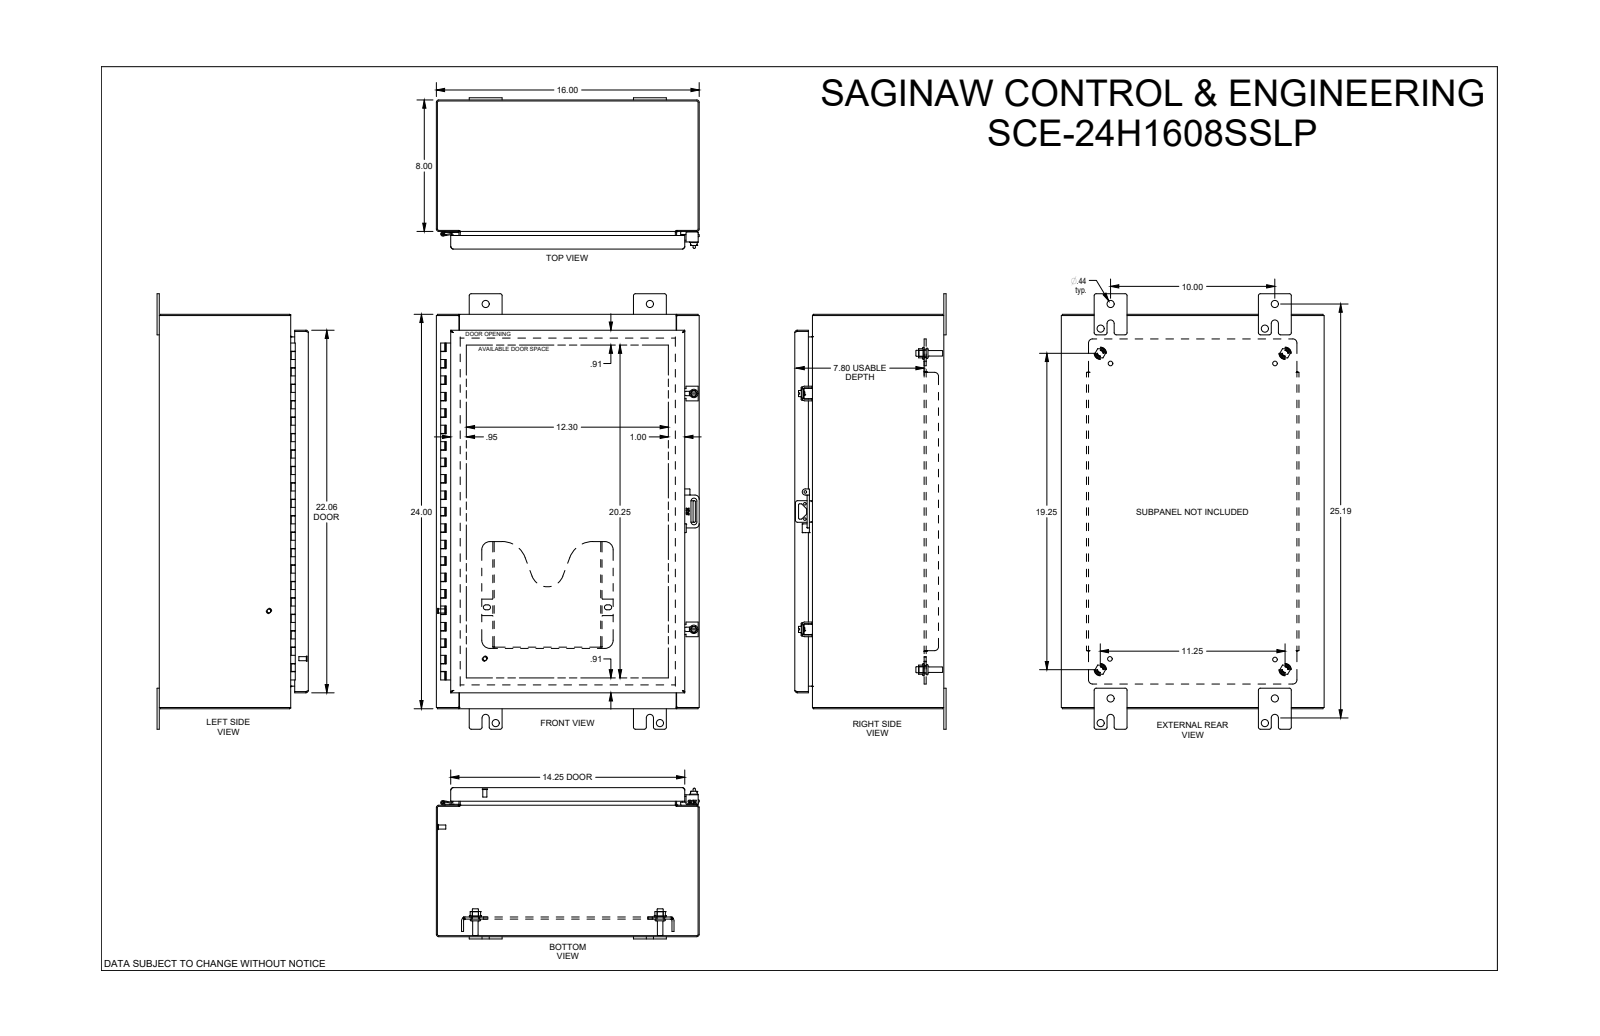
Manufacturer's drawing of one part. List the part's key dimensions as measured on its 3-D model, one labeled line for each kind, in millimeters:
Part name (STEP PRODUCT): SCE-24H1608SSLP
STEP written by: SolidWorks 2019 (CONFIG_CONTROL_DESIGN)
Units: millimetres
Bodies: 0 solids, 3160 faces (1275 planar, 660 cylindrical, 1225 other)
Overall size (bounding box): 673.1 × 406.4 × 233.9
Round holes (diameter × count): ⌀11.1 ×8, ⌀6.4 ×5, ⌀4.8 ×4, ⌀4.9 ×4, ⌀7.1 ×4, ⌀9.3 ×4, ⌀12.7 ×4, ⌀4.1 ×2, ⌀5.2 ×2, ⌀3.3 ×1, ⌀3.4 ×1
Round bosses / shafts (diameter × count): ⌀6.3 ×7, ⌀14.3 ×5, ⌀9.3 ×4, ⌀8.4 ×4, ⌀6.5 ×4, ⌀4.8 ×4, ⌀6.4 ×3, ⌀12.9 ×2
Partial cylindrical surfaces — rounded edges, fillets, slot ends (radius × count): R0.3 ×114, R0.4 ×36, R0.7 ×30, R0.8 ×27, R3.2 ×27, R1.5 ×25, R1 ×22, R1.8 ×14
Main face-to-face distances: 1.9, 404.5, 1.9, 228.5, 226.6, 228.5, 230.5, 201.2, 30.5, 28.6
Hole centre spacings: 254, 22.2, 165.1, 270.5, 473.5, 544.9, 13.1, 36.6
